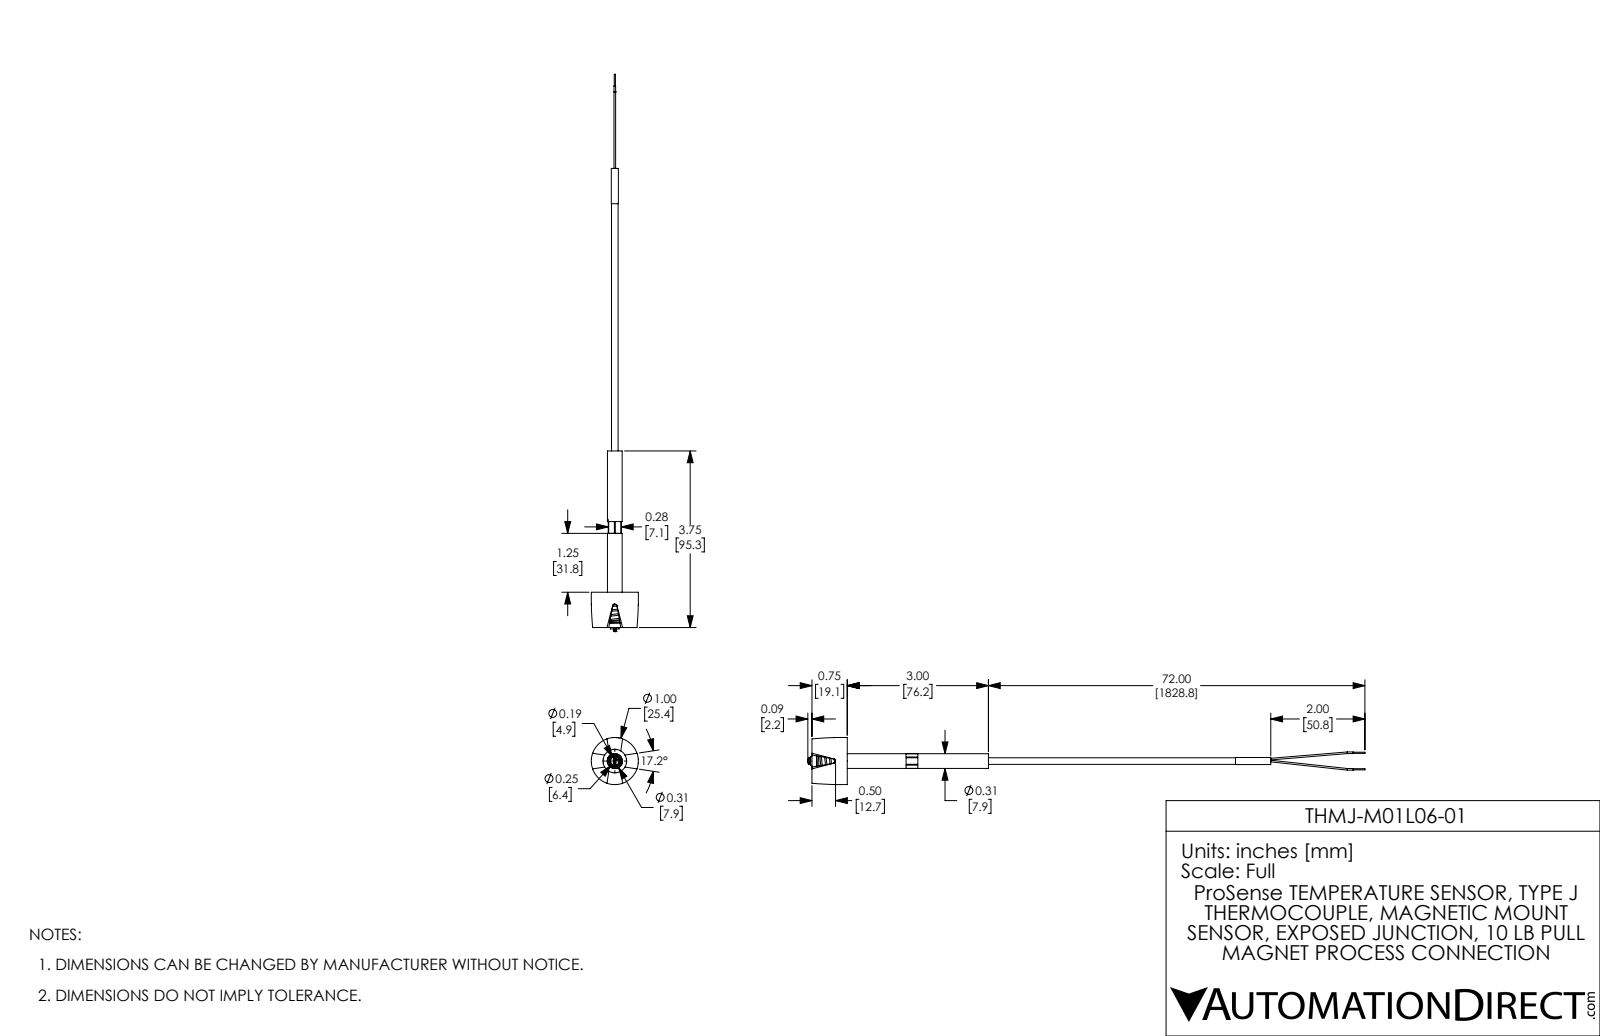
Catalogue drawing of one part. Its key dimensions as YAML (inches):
part_name: "THMJ-M01L06-01"
step_written_by: "SolidWorks 2017 (AUTOMOTIVE_DESIGN)"
units: inches
bodies: {solids: 8, faces: 114, planar: 46, cylindrical: 36, other: 32}
overall_size: [11.839, 1, 1]
volume: 0.754
surface_area: 13.68
round_holes:
  - {diameter: 0.194, count: 1}
  - {diameter: 0.253, count: 1}
  - {diameter: 0.26, count: 1}
  - {diameter: 0.5, count: 1}
round_bosses_or_shafts:
  - {diameter: 0.035, count: 4}
  - {diameter: 0.025, count: 2}
  - {diameter: 1, count: 1}
  - {diameter: 0.313, count: 1}
  - {diameter: 0.25, count: 1}
  - {diameter: 0.181, count: 1}
  - {diameter: 0.15, count: 1}
  - {diameter: 0.14, count: 1}
face_to_face_distances: [0.75, 0.25, 0.5, 0.28, 3.25, 3, 3.75, 1.5, 3.655, 0.655]
